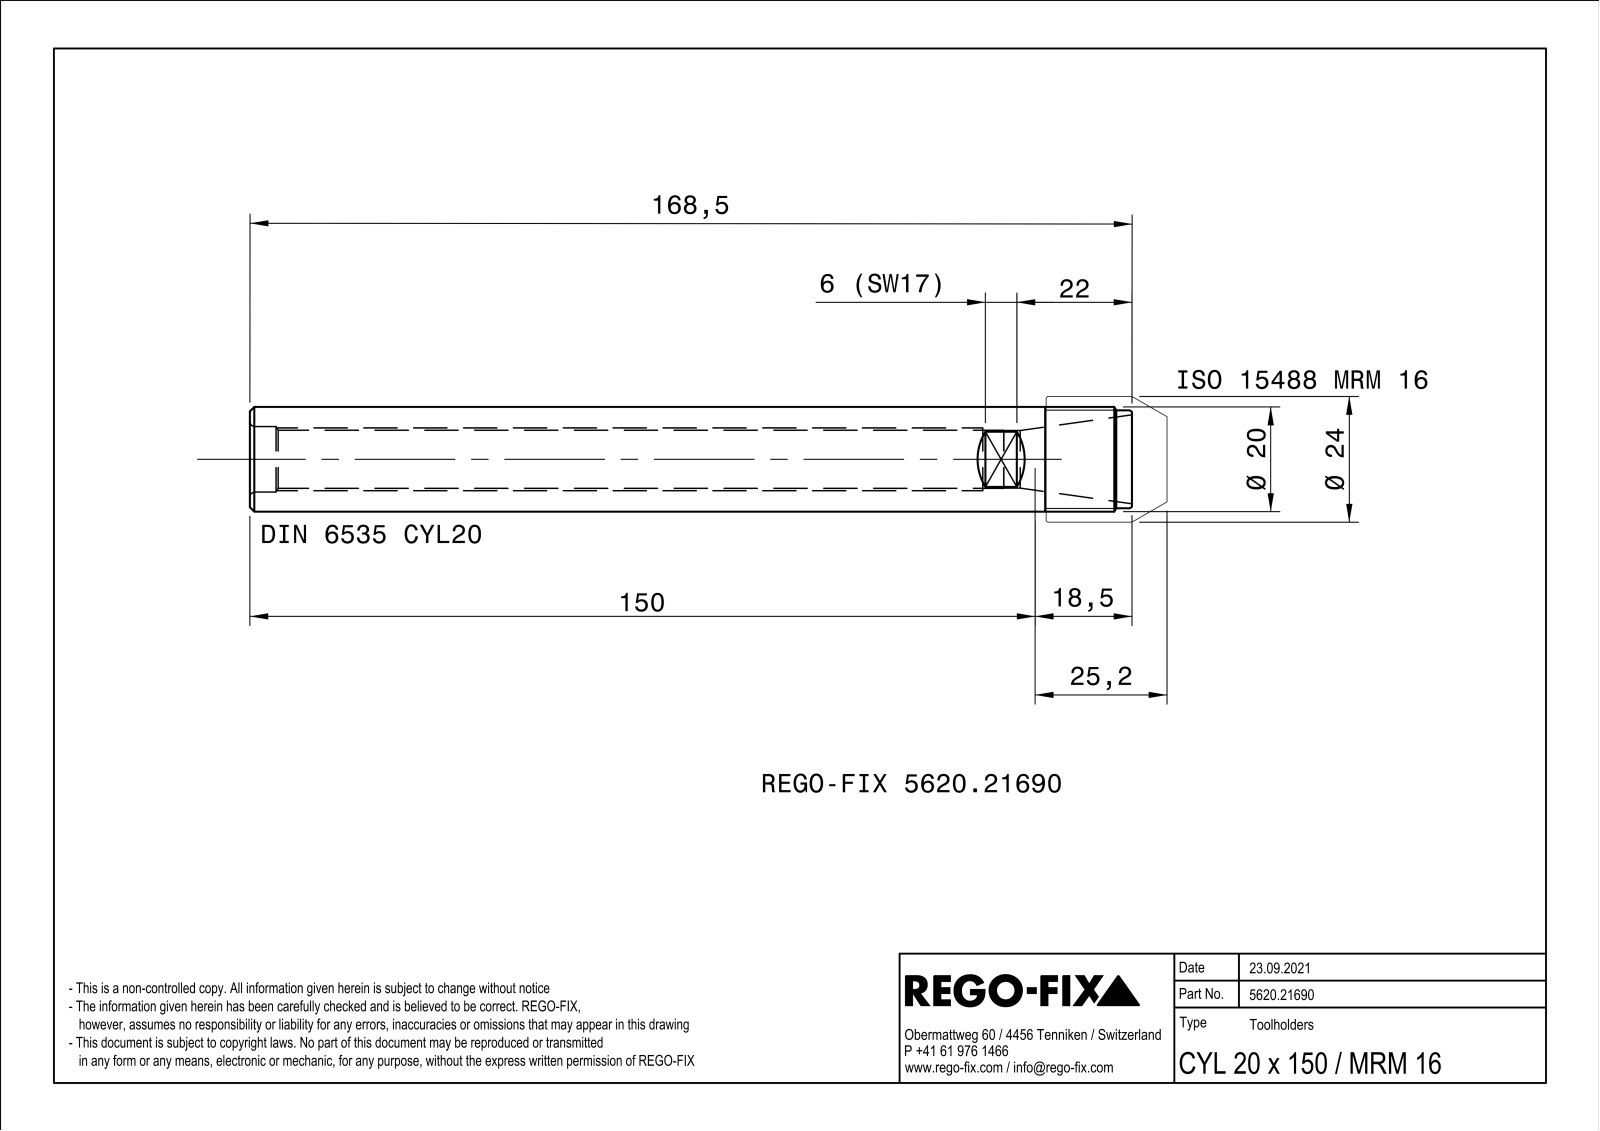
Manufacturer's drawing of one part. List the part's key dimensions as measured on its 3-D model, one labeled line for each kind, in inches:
Part name (STEP PRODUCT): 0007681
STEP written by: SIEMENS PLM Software Solid Edge ST10 (AUTOMOTIVE_DESIGN)
Units: inches
Bodies: 1 solid, 23 faces (8 planar, 7 cylindrical, 8 other)
Overall size (bounding box): 6.634 × 0.787 × 0.787
Volume: 2.168 in³ · Surface area: 26.01 in²
Round holes (diameter × count): ⌀0.413 ×1, ⌀0.437 ×1, ⌀0.492 ×1
Round bosses / shafts (diameter × count): ⌀0.787 ×1, ⌀0.736 ×1
Main face-to-face distances: 0.669, 0.306, 6.634
